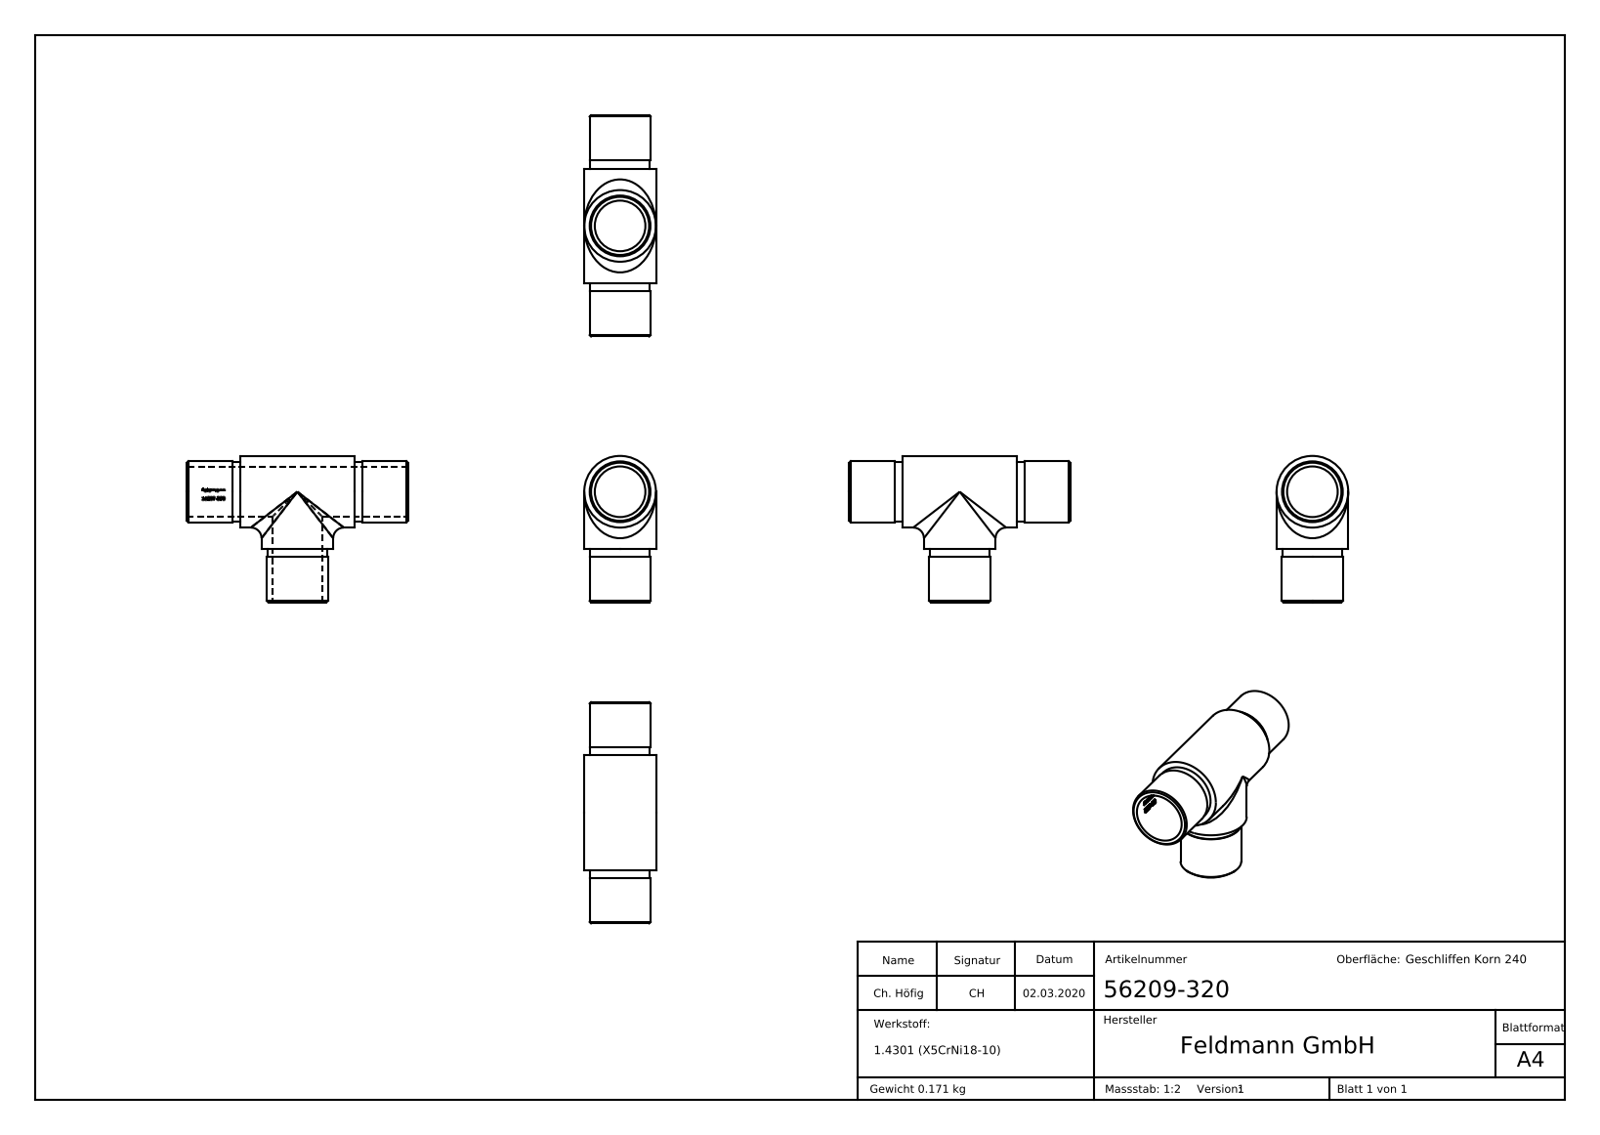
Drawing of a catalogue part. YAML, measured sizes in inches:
part_name: "56209-320"
step_written_by: "SolidWorks 2015 (CONFIG_CONTROL_DESIGN)"
units: inches
bodies: {solids: 1, faces: 251, planar: 94, cylindrical: 34, other: 123}
overall_size: [3.268, 2.163, 1.059]
volume: 1.319
surface_area: 24.55
round_holes:
  - {diameter: 0.748, count: 2}
round_bosses_or_shafts:
  - {diameter: 1.059, count: 2}
  - {diameter: 0.898, count: 2}
  - {diameter: 0.882, count: 2}
partial_cylinders:
  - {radius: 0.378, count: 1}
face_to_face_distances: [0.787, 2.48, 1.693, 3.268, 0.669, 0.118, 2.598, 1.811, 1.929, 0.015]
